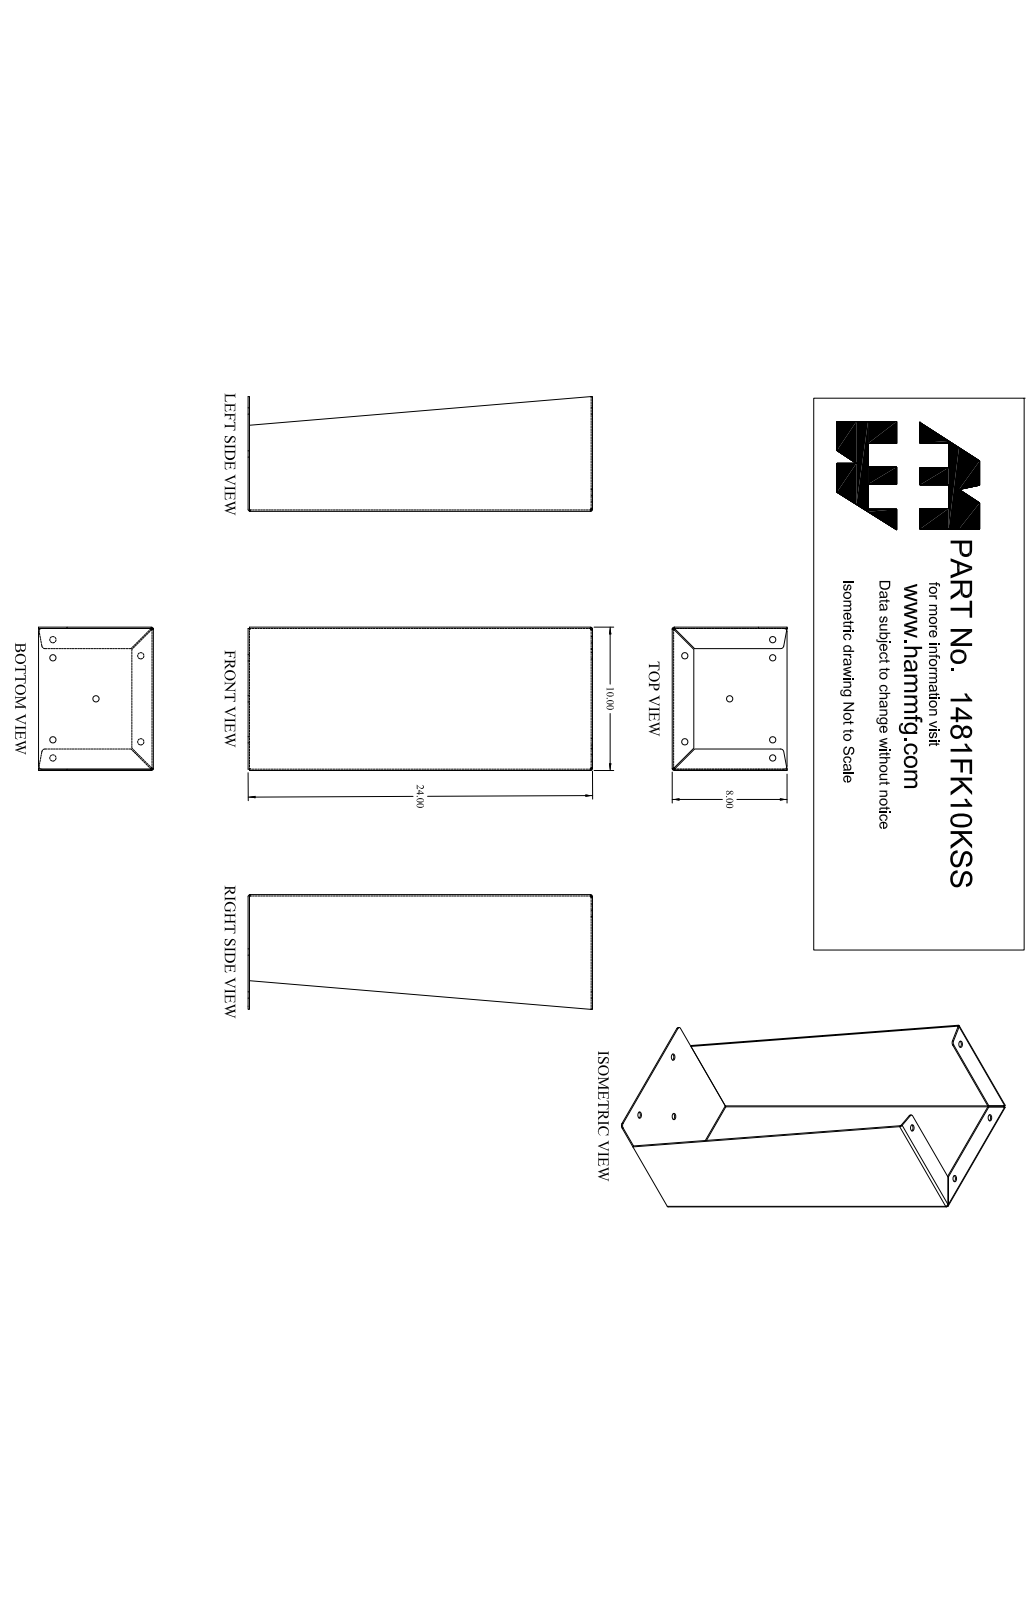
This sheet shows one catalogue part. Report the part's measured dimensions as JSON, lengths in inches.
{"part_name": "1481FK10KSS_Default", "step_written_by": "SolidWorks 2019 (CONFIG_CONTROL_DESIGN)", "units": "inches", "bodies": {"solids": 1, "faces": 78, "planar": 42, "cylindrical": 30, "other": 6}, "overall_size": [24, 10, 8], "volume_in3": 64.11, "surface_area_in2": 1362, "round_holes": [[0.437, 7]], "partial_cylinders_radius": [[0.048, 6], [0.143, 6], [0.22, 4]], "face_to_face_distances": [0.095, 9.905, 10, 9.81, 0.095, 23.81, 23.905, 23.905, 24, 1.405], "hole_center_spacings": [1.266, 4.144, 4.331, 5.101, 6.126, 6.227, 6.984, 8.476]}
